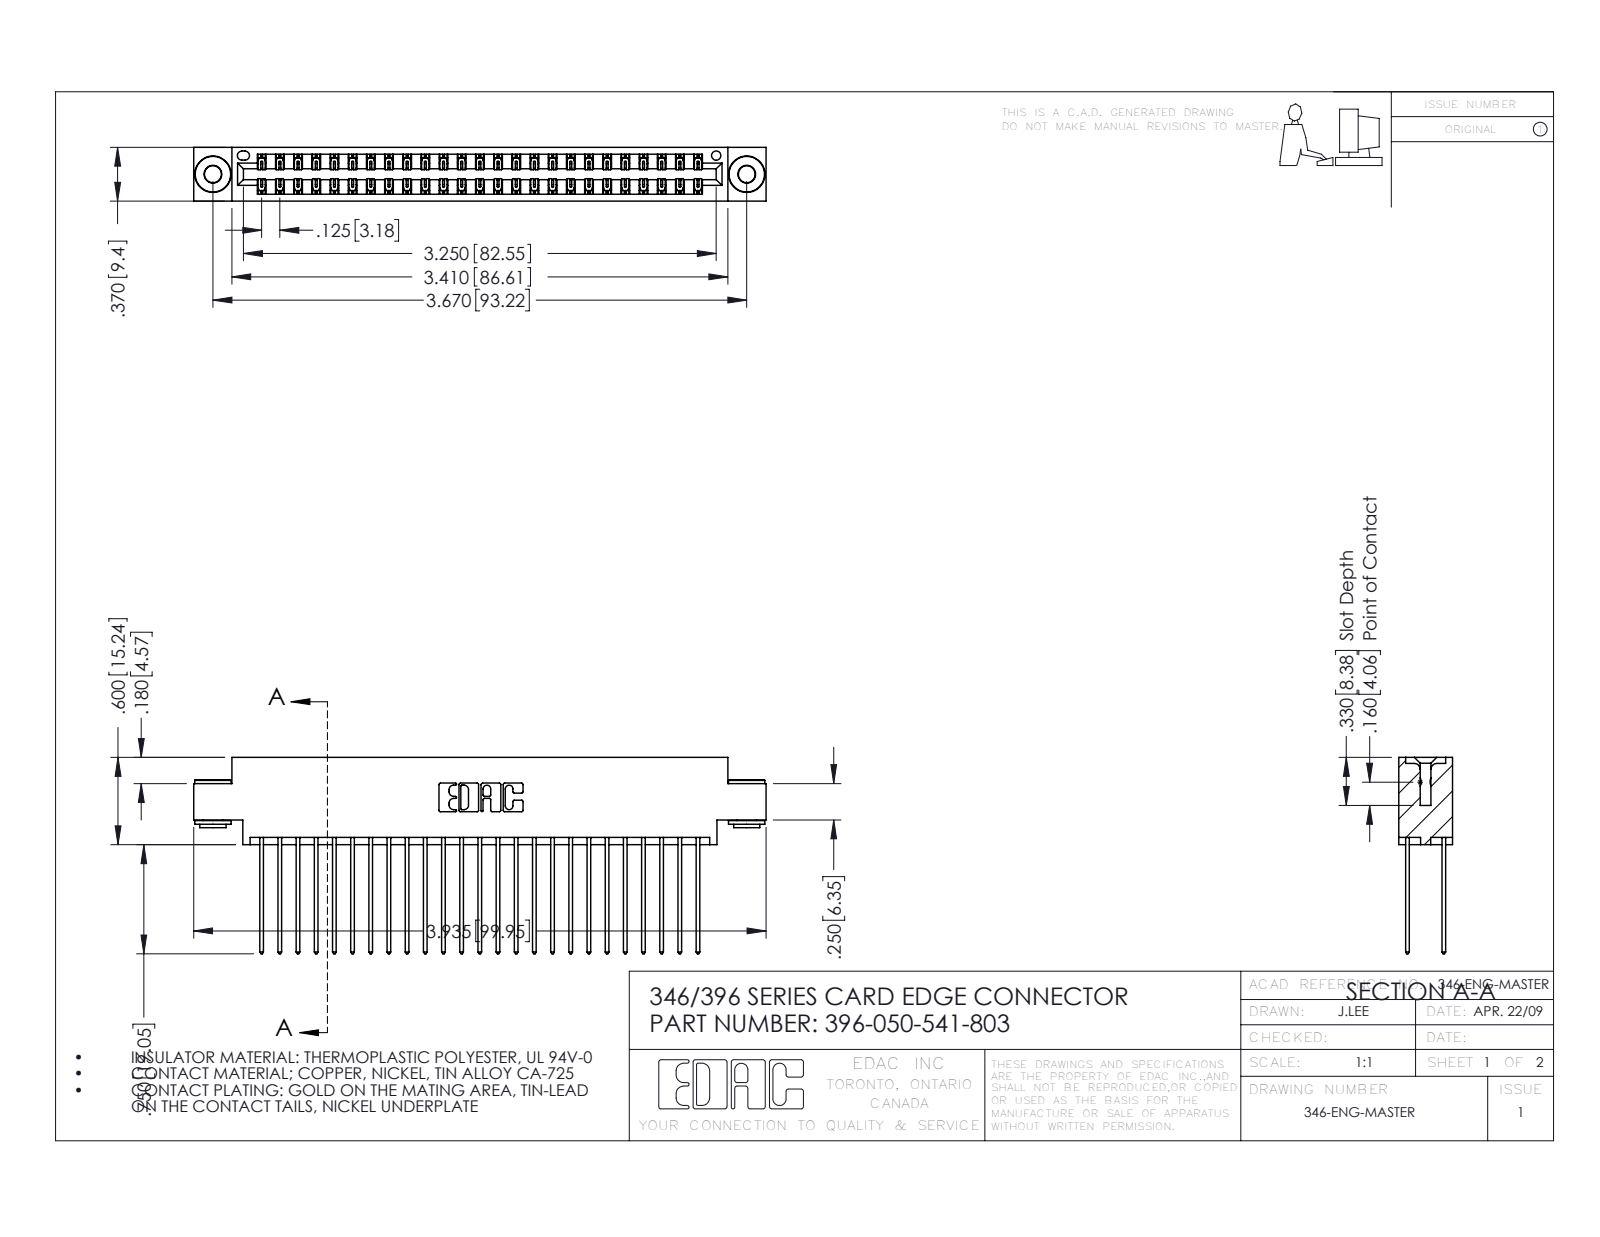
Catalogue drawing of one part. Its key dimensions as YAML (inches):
part_name: "396-050-541-803; 345-292-001_345-293-141; 345-250-002_345-250-002-102; 346 Part_0.170 Offset - 0.156 Dia-TH"
step_written_by: "SolidWorks 2016 (CONFIG_CONTROL_DESIGN)"
units: inches
bodies: {solids: 53, faces: 2764, planar: 1840, cylindrical: 916, other: 8}
overall_size: [3.935, 1.35, 0.37]
volume: 0.596
surface_area: 23.14
round_holes:
  - {diameter: 0.116, count: 2}
  - {diameter: 0.156, count: 2}
  - {diameter: 0.064, count: 1}
round_bosses_or_shafts:
  - {diameter: 0.25, count: 2}
  - {diameter: 0.18, count: 2}
  - {diameter: 0.136, count: 2}
partial_cylinders:
  - {radius: 0.006, count: 75}
  - {radius: 0.01, count: 50}
  - {radius: 0.01, count: 22}
  - {radius: 0.007, count: 6}
  - {radius: 0.031, count: 6}
  - {radius: 0.026, count: 3}
  - {radius: 0.014, count: 2}
  - {radius: 0.022, count: 2}
face_to_face_distances: [0.048, 0.322, 0.25, 0.025, 0.072, 0.298, 0.37, 0.275, 0.225, 0.148]
hole_center_spacings: [0.246, 3.462, 3.67]
